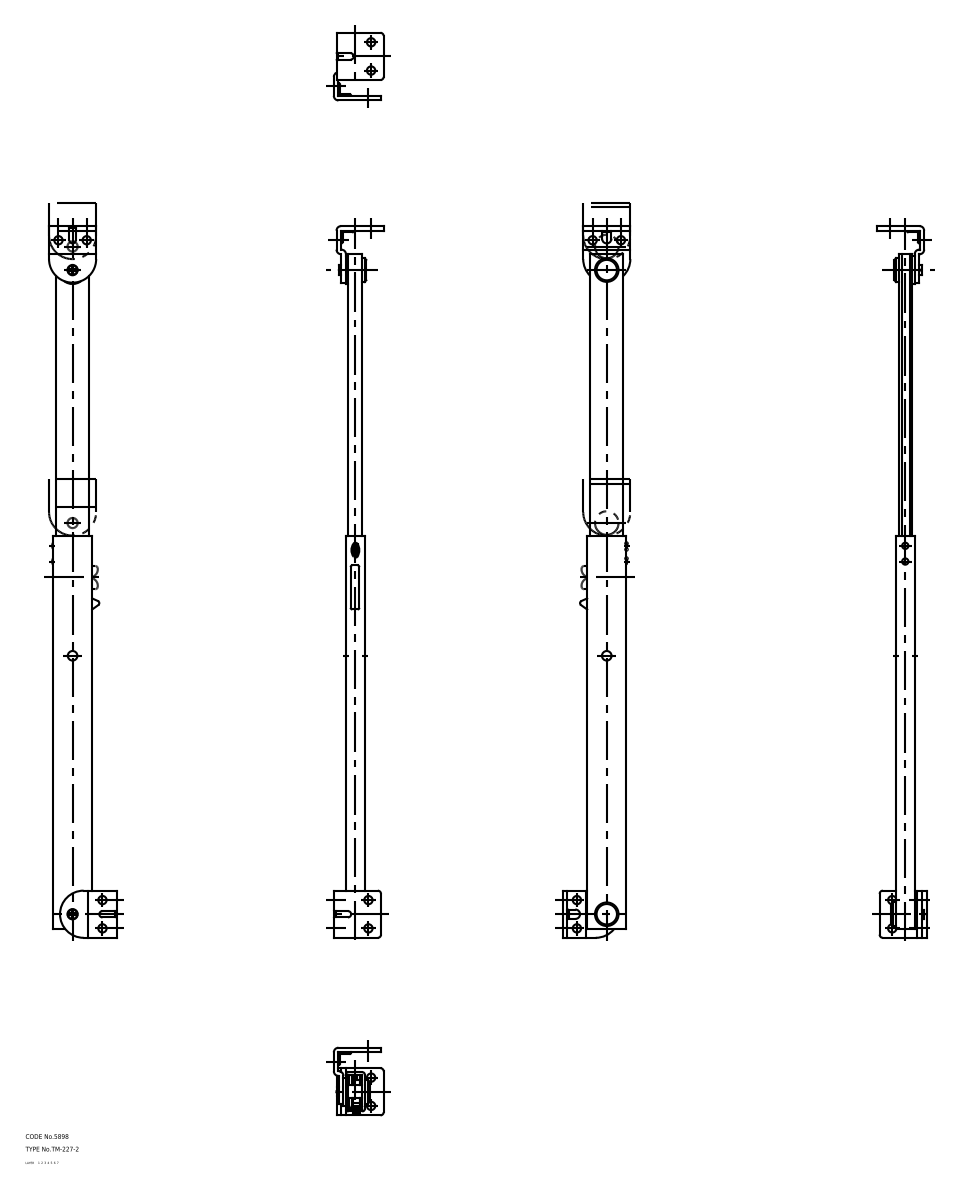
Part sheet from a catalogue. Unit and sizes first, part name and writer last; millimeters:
Units: millimetres
Overall size (bounding box): 453 × 43 × 31.7
Volume: 57 925 mm³ · Surface area: 69 079 mm²
Bodies: 10 solids, 236 faces (0 planar, 0 cylindrical, 236 other)
Part name (STEP PRODUCT): shaft_mr; washer_mr-1; washer_mr; bracket_mr-1 (+7 more)
STEP written by: CADfix (AUTOMOTIVE_DESIGN)
